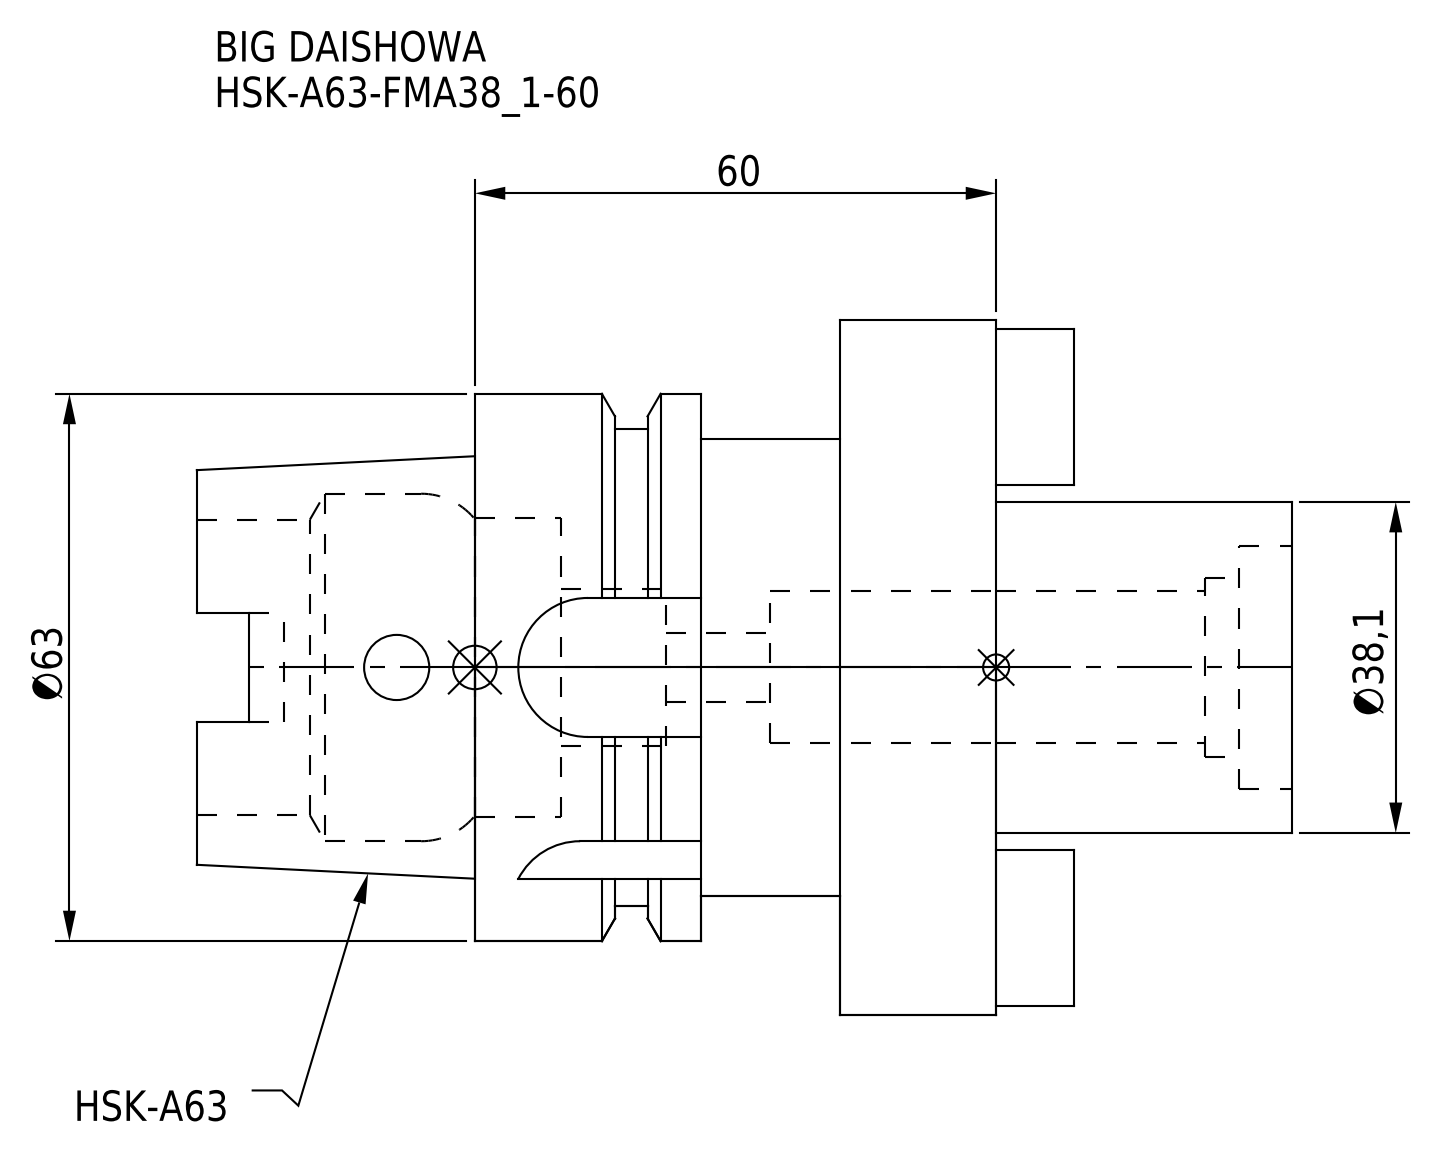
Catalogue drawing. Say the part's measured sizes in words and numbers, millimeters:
The part is named "HSK-A63-FMA38_1-60". Its 3-D file was written by "CREO PARAMETRIC BY PTC INC, 2016380 (AUTOMOTIVE_DESIGN)". It is 1 solid with 98 faces: 46 planar, 40 cylindrical and 12 other. Overall it measures 126 by 80 by 80 millimeters. Its volume is 233 521 cubic millimeters and its surface area 44 345 square millimeters. Round holes: 1 of diameter 7.5, 1 of diameter 8, 1 of diameter 17.5, 1 of diameter 18, 1 of diameter 20.5, 1 of diameter 28, 1 of diameter 34, 1 of diameter 34.5, 1 of diameter 40. Round bosses or shafts: 1 of diameter 80, 1 of diameter 63, 1 of diameter 55, 1 of diameter 52.6, 1 of diameter 38.1. Partial cylindrical surfaces (rounded edges, fillets, slot ends): 2 of radius 8, 1 of radius 9. The main face-to-face distances are 18, 60, 42, 34, 26, 16, 50.05, 32.05, 16.05, 9.95.
